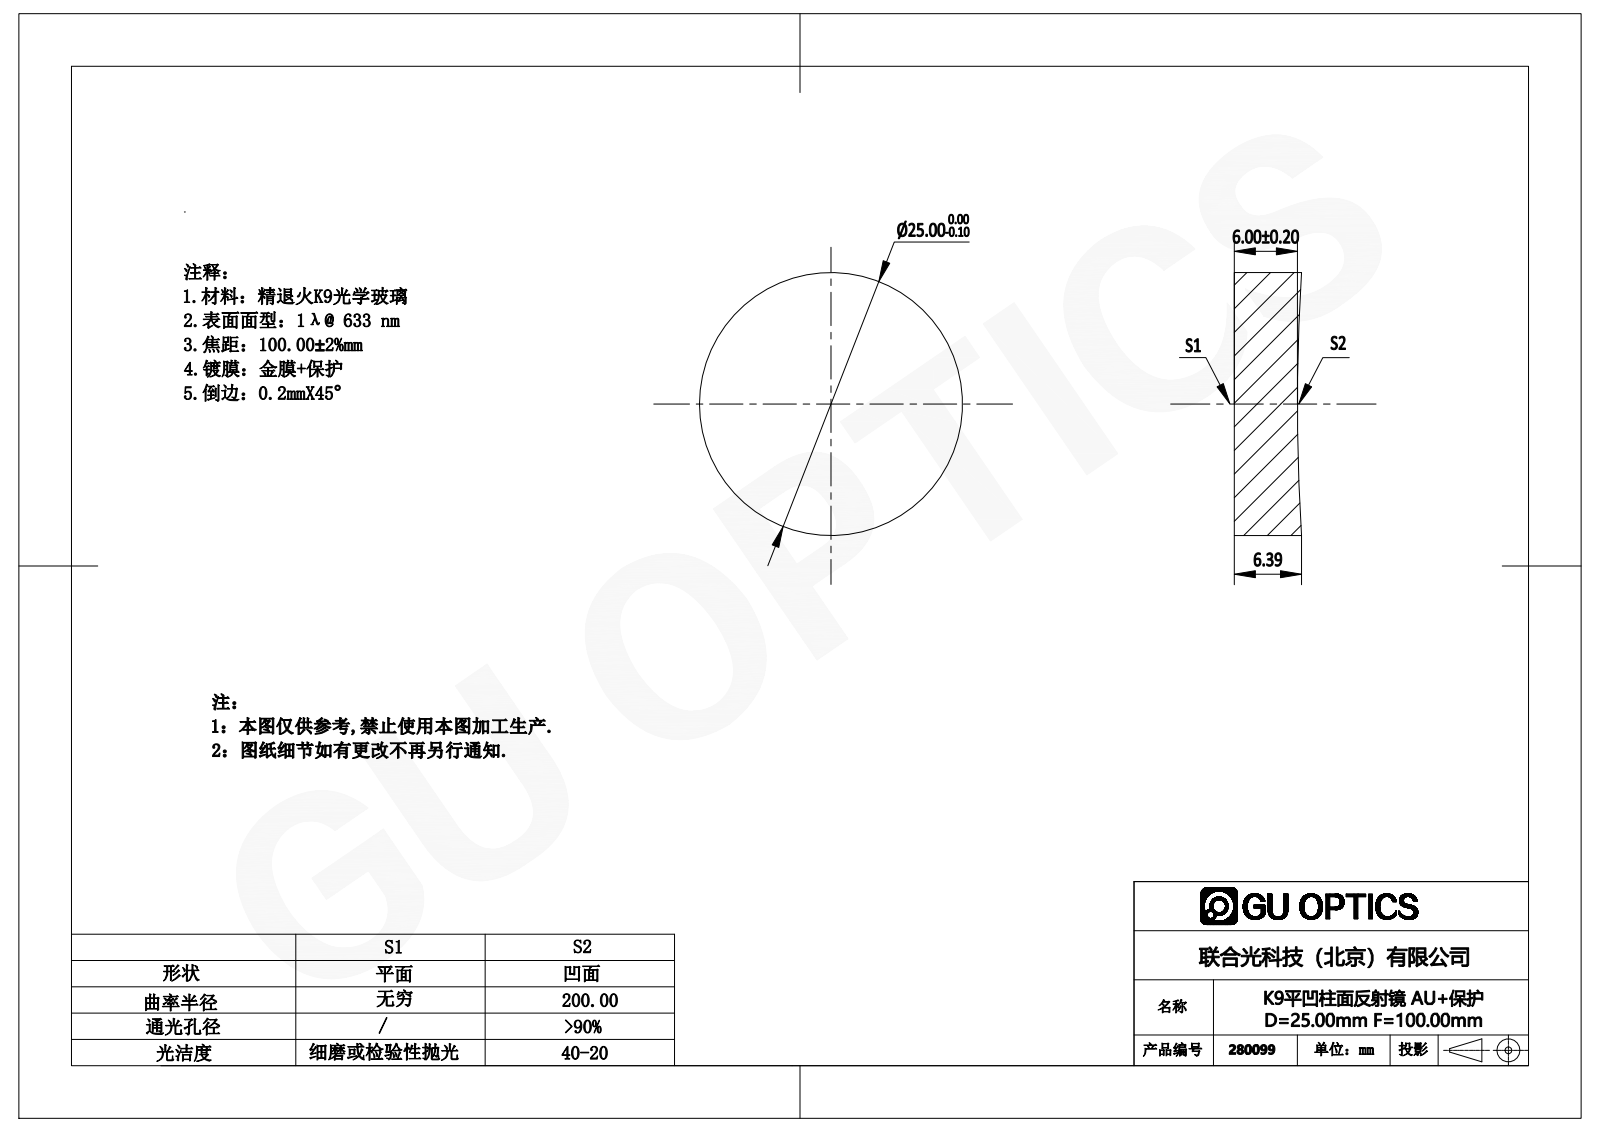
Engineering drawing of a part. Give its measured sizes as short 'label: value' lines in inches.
name: 280011
written by: SolidWorks 2020 (CONFIG_CONTROL_DESIGN)
unit: in
bodies: 1 solid, 3 faces (1 planar, 2 cylindrical, 0 other)
size: 0.984 × 0.984 × 0.252
volume: 0.183 in³; area: 2.277 in²
bosses: 1× ⌀0.984
rounds: 1× R7.874
